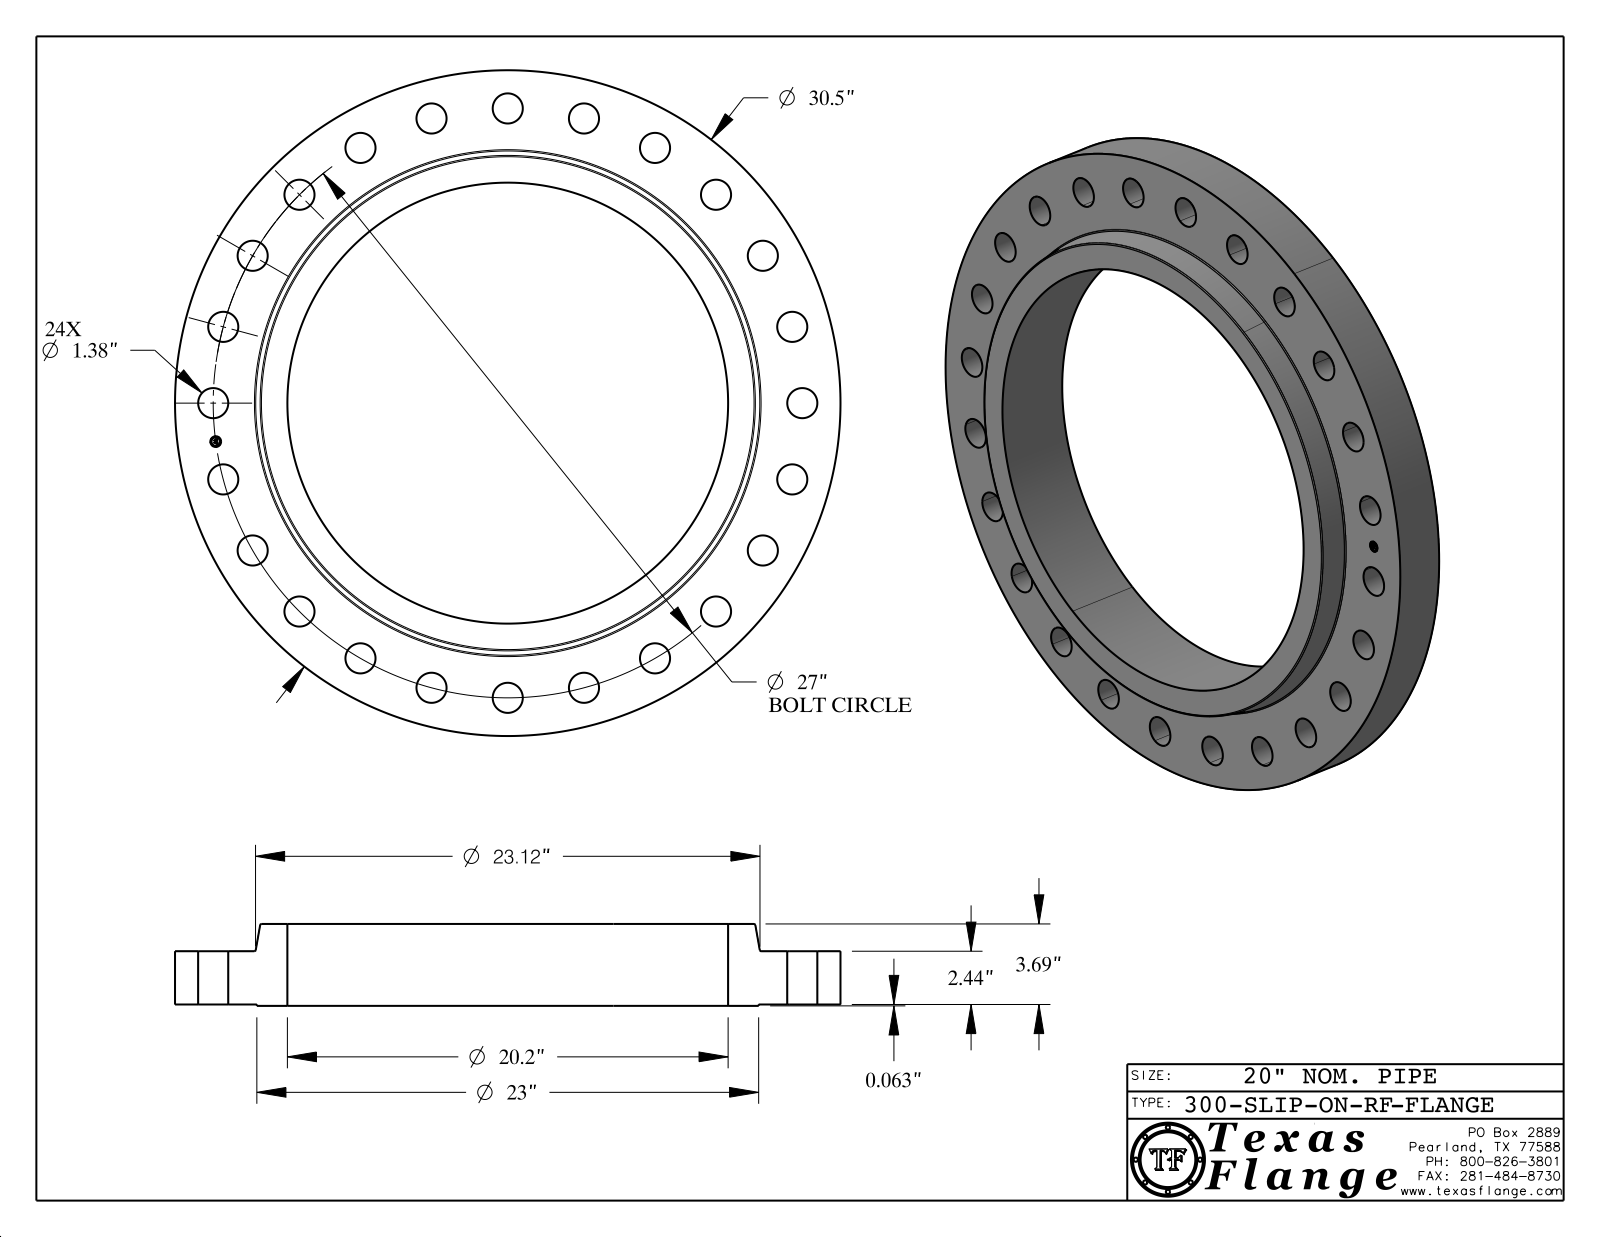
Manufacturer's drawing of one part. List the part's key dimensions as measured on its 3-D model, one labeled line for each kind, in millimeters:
Part name (STEP PRODUCT): 300-SLIP-ON-RF
STEP written by: CATIA V5 STEP AP214 (AUTOMOTIVE_DESIGN)
Units: millimetres
Bodies: 1 solid, 449 faces (369 planar, 74 cylindrical, 6 other)
Overall size (bounding box): 774.7 × 774.7 × 95.3
Volume: 16 930 000 mm³ · Surface area: 1 001 000 mm²
Round holes (diameter × count): ⌀35.1 ×24, ⌀12.6 ×1, ⌀513.1 ×1
Round bosses / shafts (diameter × count): ⌀0.8 ×8, ⌀774.7 ×1, ⌀584.2 ×1, ⌀9.9 ×1
Main face-to-face distances: 62, 1.6, 63.6, 95.3, 93.7, 31.8, 63.2, 61.6, 0.4, 32.1
Hole centre spacings: 342.9, 89.5, 177.5, 262.5, 417.5, 633.6, 679.9, 544.1
